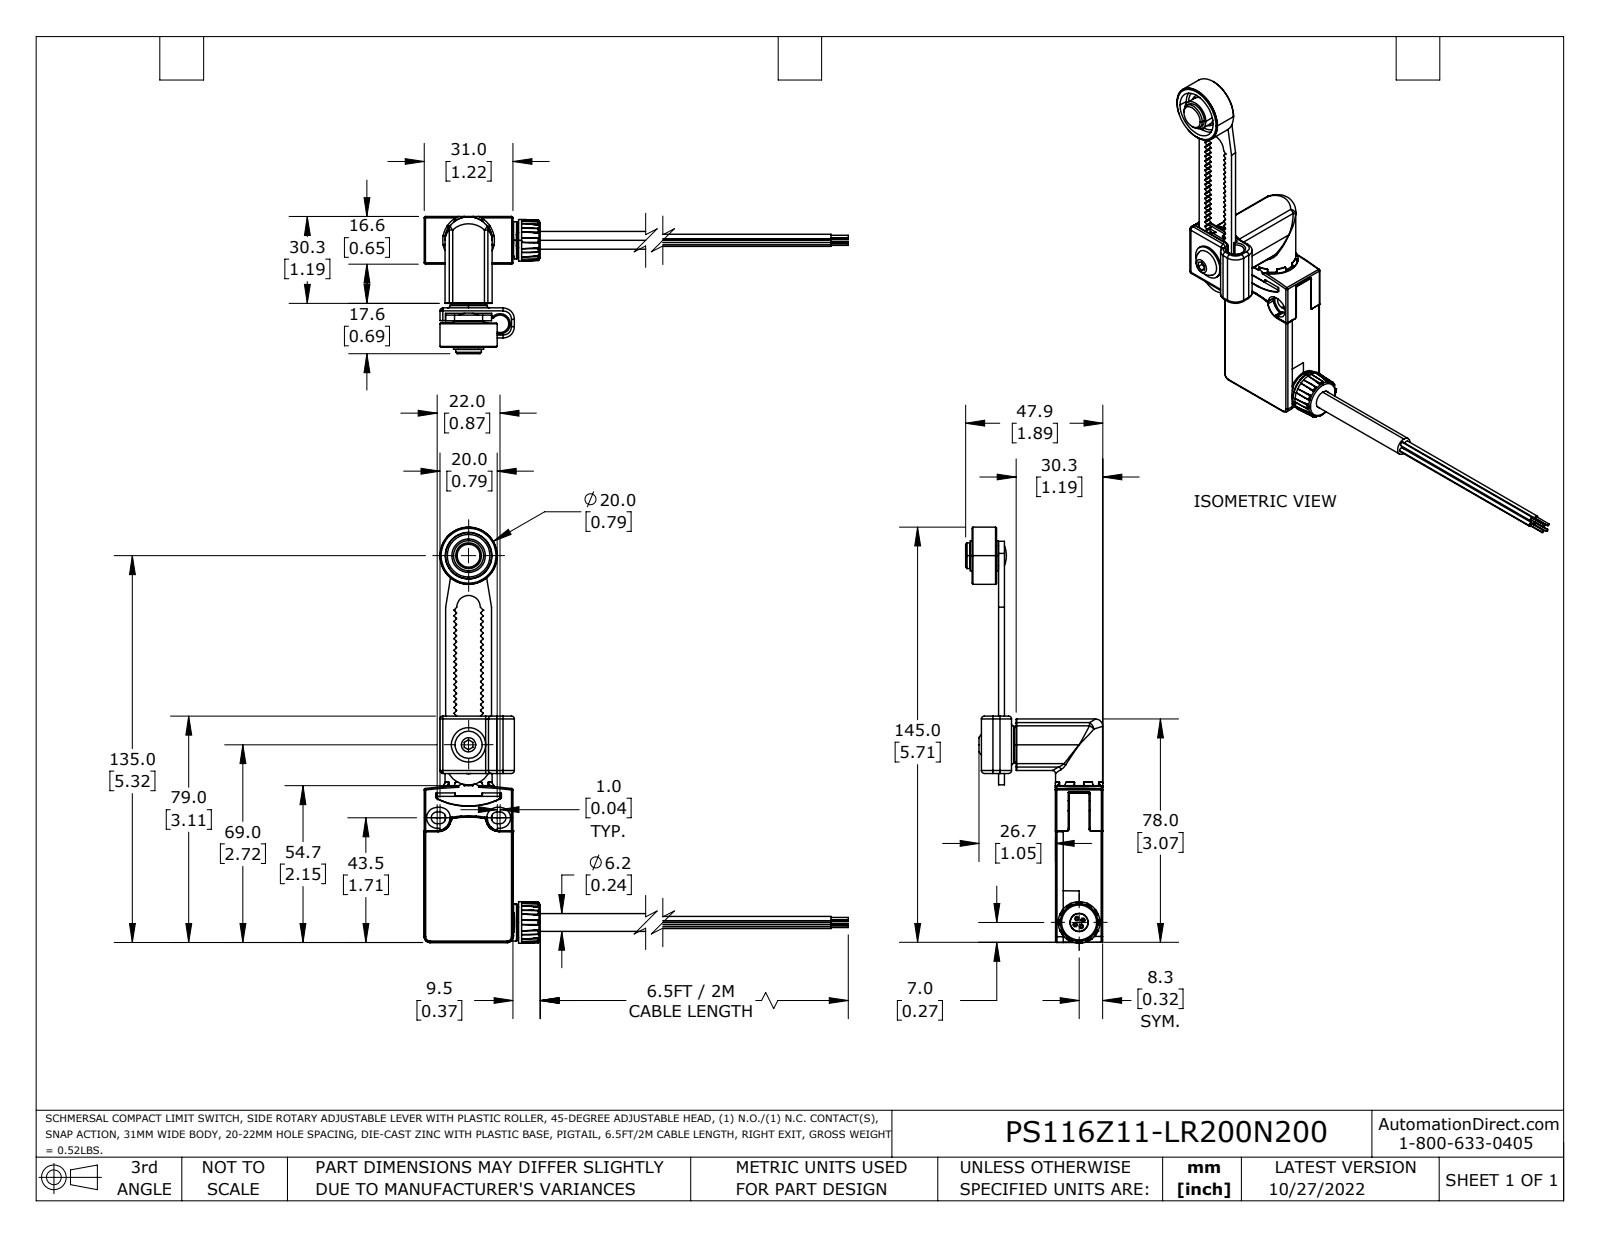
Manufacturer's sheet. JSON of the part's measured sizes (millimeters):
{"part_name": "PS116Z11-LR200N200_Default", "step_written_by": "SolidWorks 2021 (CONFIG_CONTROL_DESIGN)", "units": "millimeters", "bodies": {"solids": 1, "faces": 1556, "planar": 489, "cylindrical": 714, "other": 353}, "overall_size": [150.5, 145.3, 47.9], "volume_mm3": 44290, "surface_area_mm2": 22480, "round_holes": [[12.2, 2], [2, 1], [6.1, 1], [6.4, 1], [8, 1], [14.5, 1], [14.8, 1]], "round_bosses_or_shafts": [[1.5, 4], [0.8, 4], [13, 2], [20, 1], [16.5, 1], [14.5, 1], [14.4, 1], [13.3, 1]], "partial_cylinders_radius": [[0.2, 253], [0.1, 61], [0.5, 37], [1, 27], [2, 12], [0.4, 10], [0.3, 6], [3, 5]], "face_to_face_distances": [16.5, 19.8, 2, 36.3, 34.3, 17.9, 16.6, 2.5, 4.5, 5.1], "hole_center_spacings": [31.2, 41, 66]}
